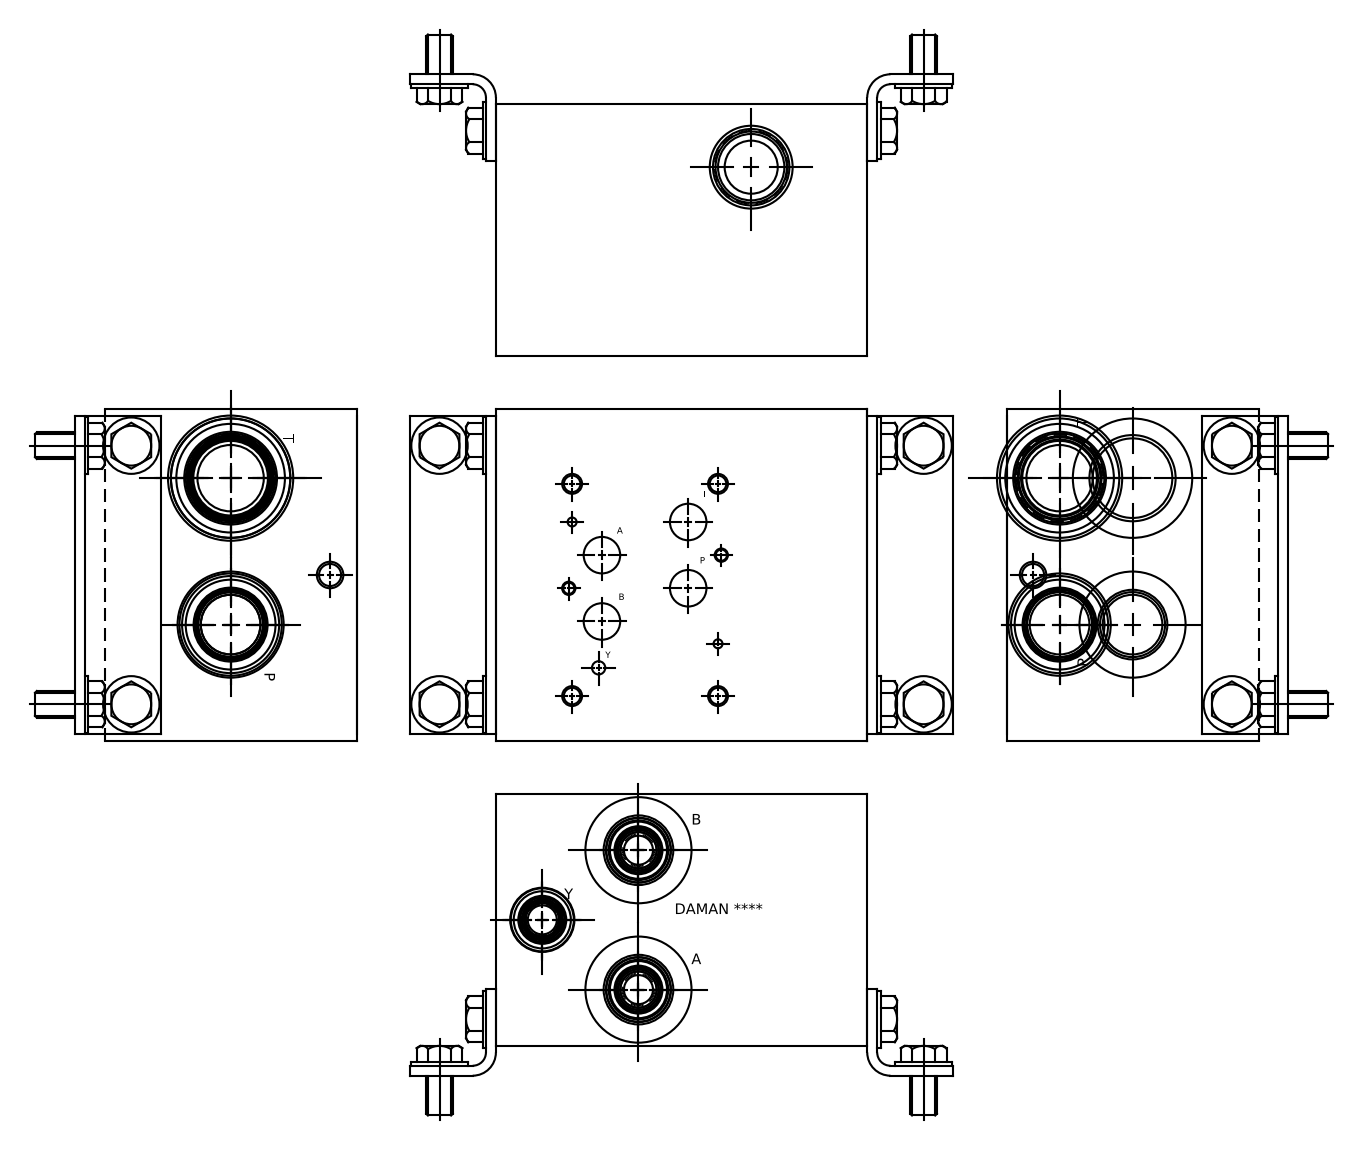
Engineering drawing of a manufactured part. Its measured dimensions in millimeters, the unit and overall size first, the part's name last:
Units: millimetres
Overall size (bounding box): 177.8 × 158.75 × 120.65
Round holes (diameter × count): ⌀19.05 ×5, ⌀7.92 ×4, ⌀9.53 ×4, ⌀10.72 ×3, ⌀12.7 ×3, ⌀31.27 ×3, ⌀33.34 ×3, ⌀33.76 ×3, ⌀49.12 ×3, ⌀4.37 ×2, ⌀5.11 ×2, ⌀6.35 ×2
Main face-to-face distances: 120.65, 158.75, 177.8, 0.79, 177.01, 157.96, 176.22, 19.05, 19.84, 157.17
Hole centre spacings: 44.23, 22.45, 31.75, 69.85, 101.6, 123.29, 18.26, 18.52
Volume: 3 089 000 mm³ · Surface area: 180 292 mm²
Bodies: 1 solid, 581 faces (348 planar, 72 cylindrical, 161 other)
Part name (STEP PRODUCT): Part_AD07HP014S_S_3D
STEP written by: Autodesk Inventor 2020 (AUTOMOTIVE_DESIGN)
